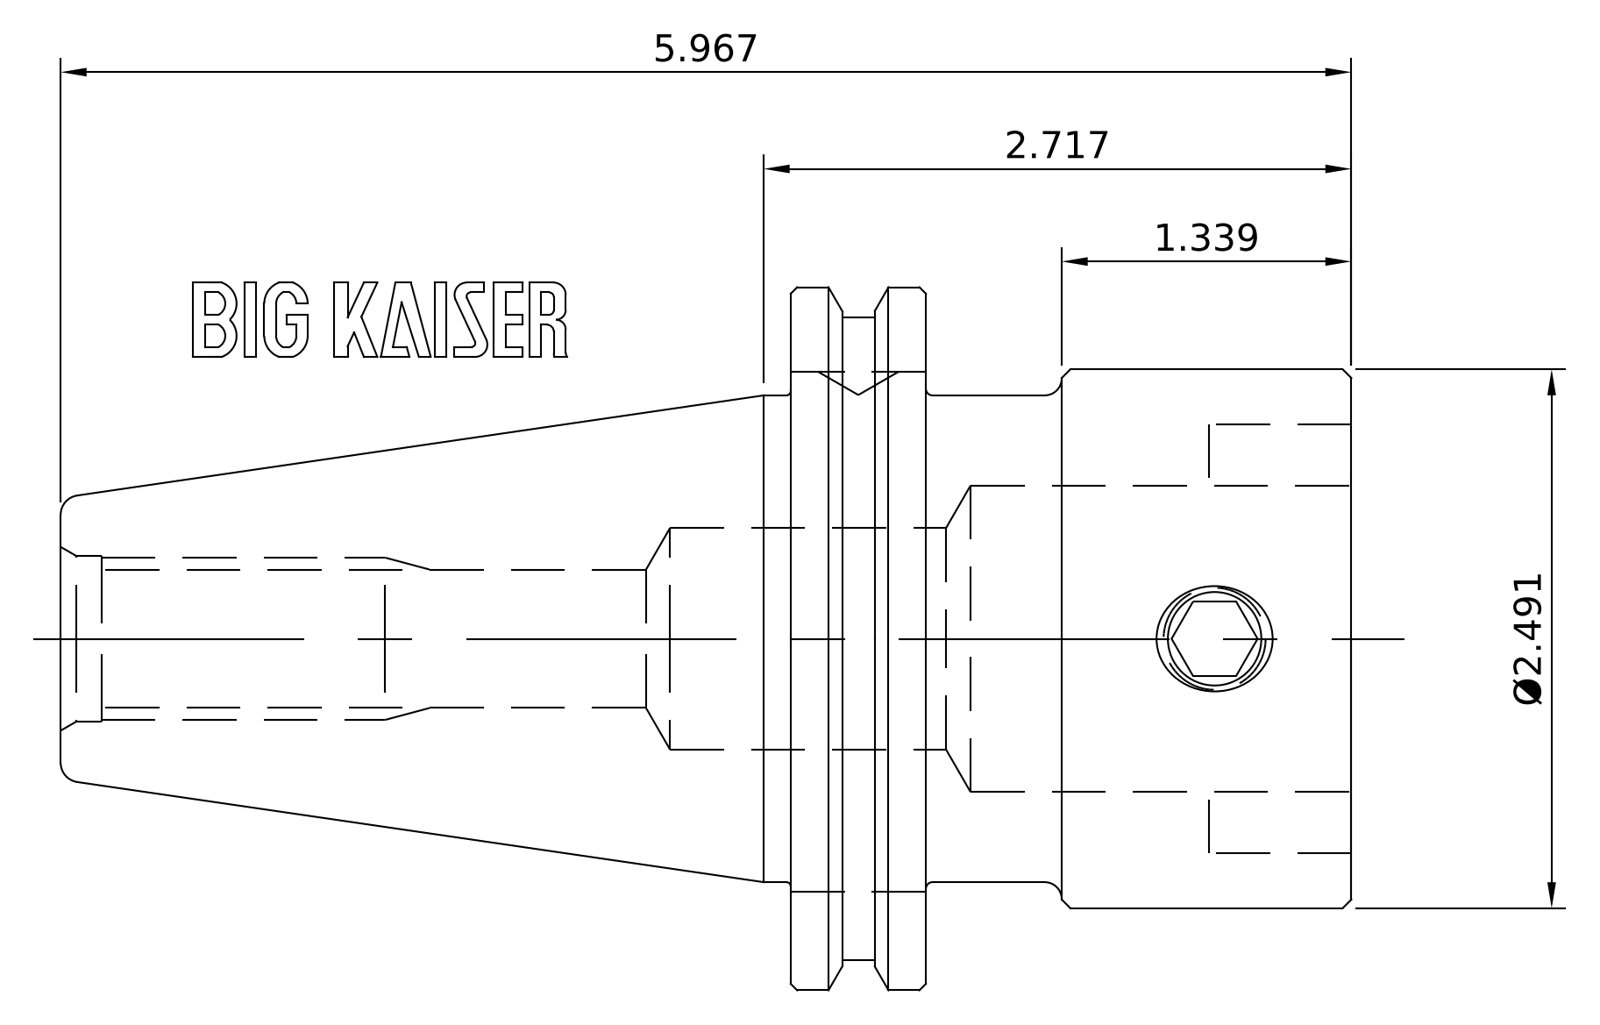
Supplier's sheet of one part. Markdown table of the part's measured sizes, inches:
| quantity | value |
| --- | --- |
| part name | 11.326.562 |
| STEP written by | SolidWorks 2021 (CONFIG_CONTROL_DESIGN) |
| units | inches |
| bodies | 1 solid, 16 faces (7 planar, 6 cylindrical, 3 other) |
| overall size | 5.966 × 3.25 × 3.25 |
| volume | 22.71 in³ |
| surface area | 58.01 in² |
| round bosses / shafts (diameter × count) | 3.25 × 1, 2.969 × 1, 2.5 × 1, 2.25 × 1 |
| main face-to-face distances | 2.591, 1.966, 0.625, 5.966, 4, 3.375, 1.338, 0.628, 1.253, 4.628 |
